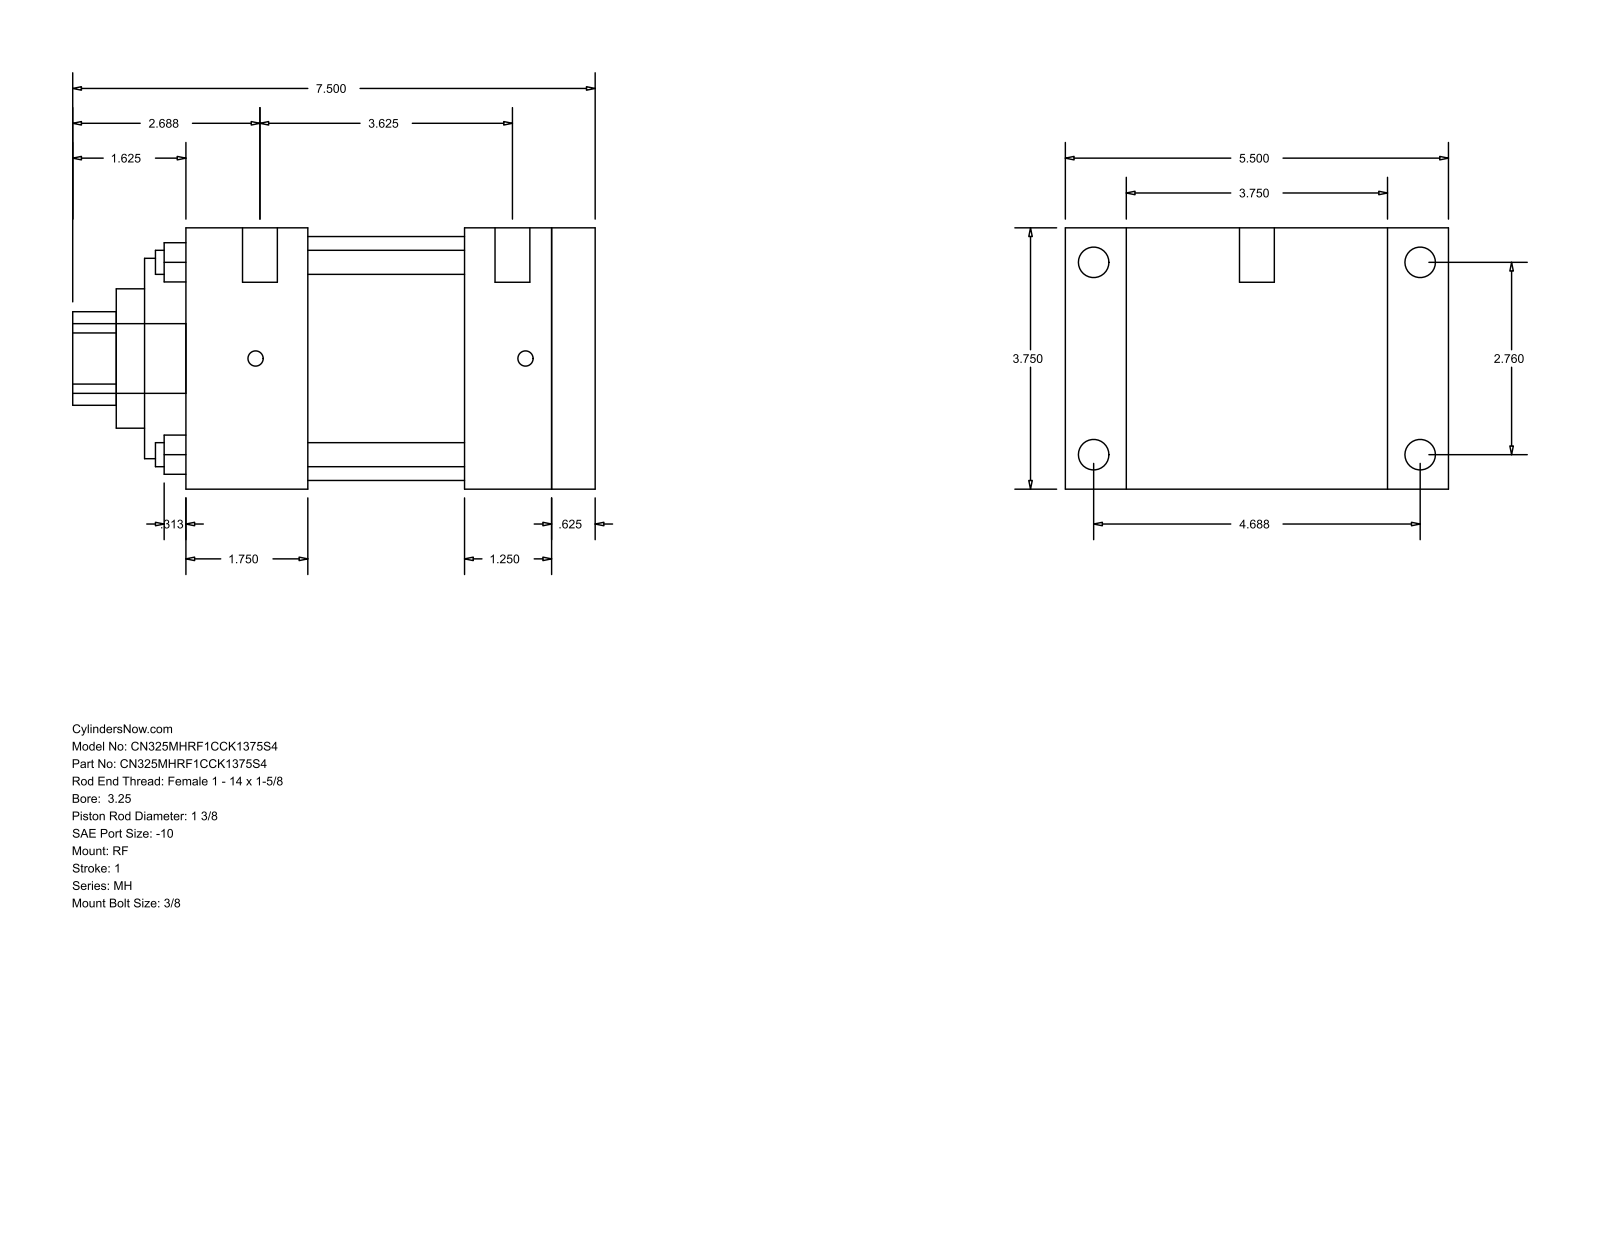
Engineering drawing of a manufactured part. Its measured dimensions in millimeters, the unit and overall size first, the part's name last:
Units: millimetres
Overall size (bounding box): 190.5 × 139.7 × 95.25
Round holes (diameter × count): ⌀8.76 ×4, ⌀34.92 ×1, ⌀50.8 ×1, ⌀73.03 ×1, ⌀88.9 ×1
Round bosses / shafts (diameter × count): ⌀11.13 ×4, ⌀5.56 ×4, ⌀12.7 ×2, ⌀25.4 ×1
Partial cylindrical surfaces — rounded edges, fillets, slot ends (radius × count): R17.06 ×1
Main face-to-face distances: 95.24, 149.23, 15.88, 133.35, 22.23, 117.47, 44.45, 88.9, 104.78, 101.61
Hole centre spacings: 49.57, 70.1, 99.14
Bodies: 0 solids, 94 faces (65 planar, 29 cylindrical, 0 other)
Part name (STEP PRODUCT): MH_RF__0325_1.375
STEP written by: GSSL Pune (CONFIG_CONTROL_DESIGN)
